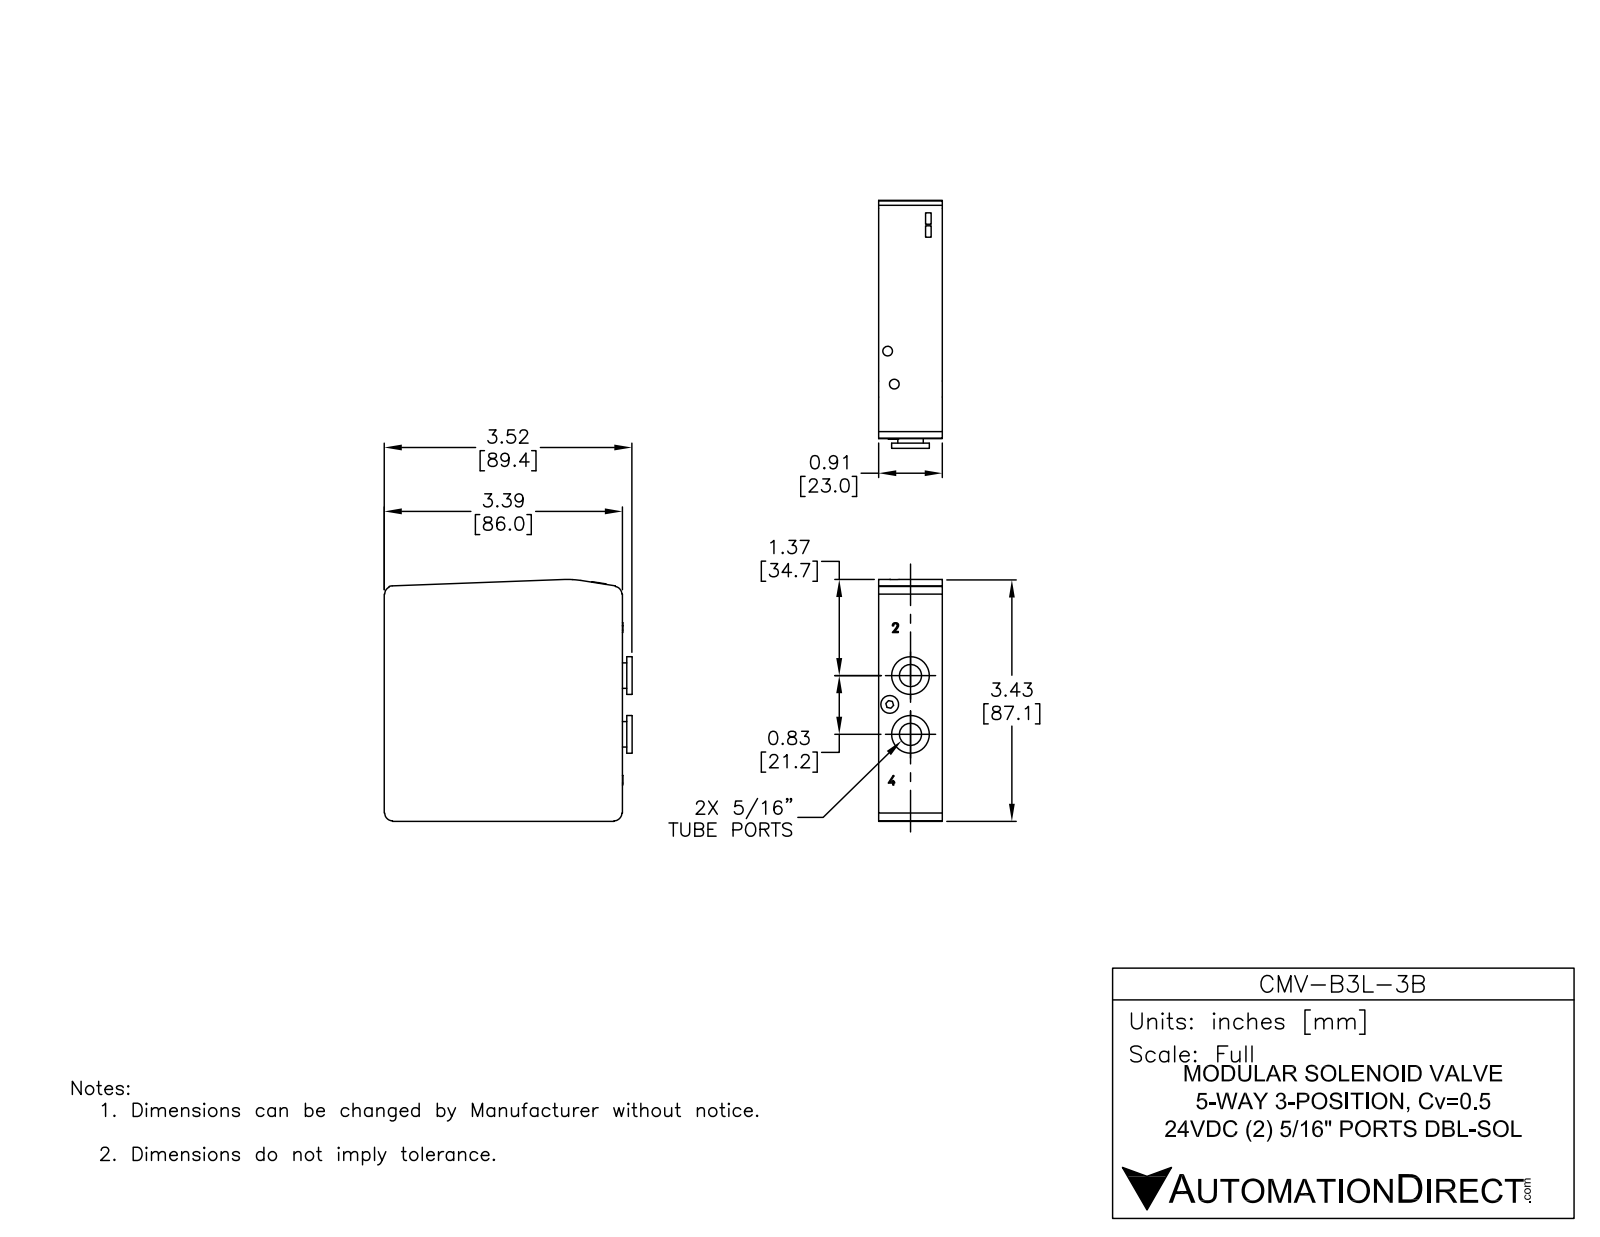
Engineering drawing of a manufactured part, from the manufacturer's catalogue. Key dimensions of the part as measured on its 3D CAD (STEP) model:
Part name (STEP PRODUCT): CMV-B3L-3B
STEP written by: SolidWorks 2013 (AUTOMOTIVE_DESIGN)
Units: millimetres
Bodies: 75 solids, 1177 faces (882 planar, 162 cylindrical, 133 other)
Overall size (bounding box): 89.5 × 87.3 × 31.43
Volume: 154 040 mm³ · Surface area: 54 388 mm²
Round holes (diameter × count): ⌀4.4 ×4, ⌀5.25 ×4, ⌀3.35 ×2, ⌀6.5 ×2, ⌀9.75 ×2, ⌀14 ×2, ⌀18 ×2, ⌀3.6 ×1, ⌀6.25 ×1
Round bosses / shafts (diameter × count): ⌀4 ×4, ⌀1.5 ×4, ⌀15.25 ×2, ⌀11 ×2, ⌀6.25 ×2, ⌀5.75 ×2, ⌀4.2 ×2, ⌀3.5 ×1
Partial cylindrical surfaces — rounded edges, fillets, slot ends (radius × count): R2.35 ×12, R0.78 ×4, R1.5 ×4, R2.8 ×4, R0.15 ×2, R0.25 ×2, R1 ×2, R2.25 ×2
Main face-to-face distances: 22.5, 12.5, 10, 83, 3, 1, 65.12, 50.25, 32.75, 53.25
Hole centre spacings: 9.7, 11.99, 12.17, 16, 22.17, 31.45, 31.52, 39.5
